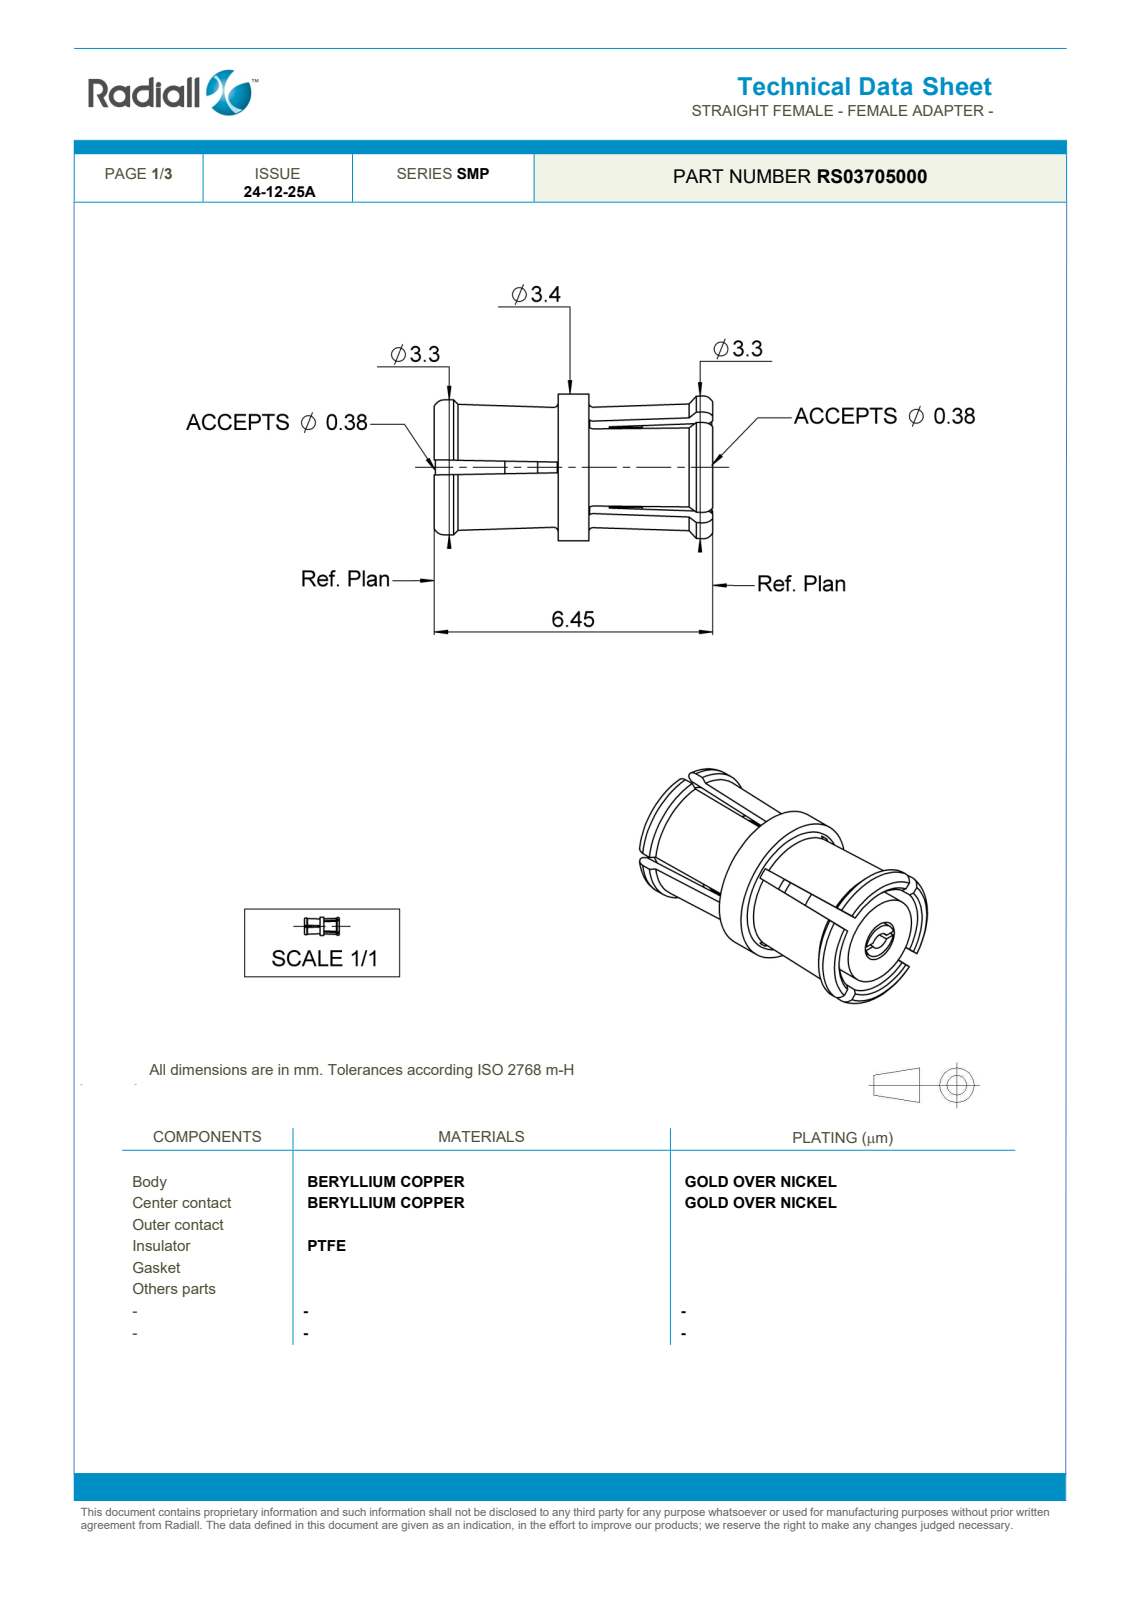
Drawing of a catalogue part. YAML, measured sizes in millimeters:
part_name: "R222.705.000 B"
step_written_by: "SolidWorks 2011 (CONFIG_CONTROL_DESIGN)"
units: millimeters
bodies: {solids: 1, faces: 142, planar: 54, cylindrical: 19, other: 69}
overall_size: [6.45, 3.4, 3.4]
volume: 33
surface_area: 177
round_holes:
  - {diameter: 0.95, count: 1}
round_bosses_or_shafts:
  - {diameter: 3.4, count: 1}
  - {diameter: 3.15, count: 1}
  - {diameter: 2.07, count: 1}
  - {diameter: 1.85, count: 1}
partial_cylinders:
  - {radius: 1.21, count: 1}
face_to_face_distances: [2.84, 3.56, 2.37, 4.03, 0.47, 1.19, 6.4, 0.72, 1.66, 3.58]
